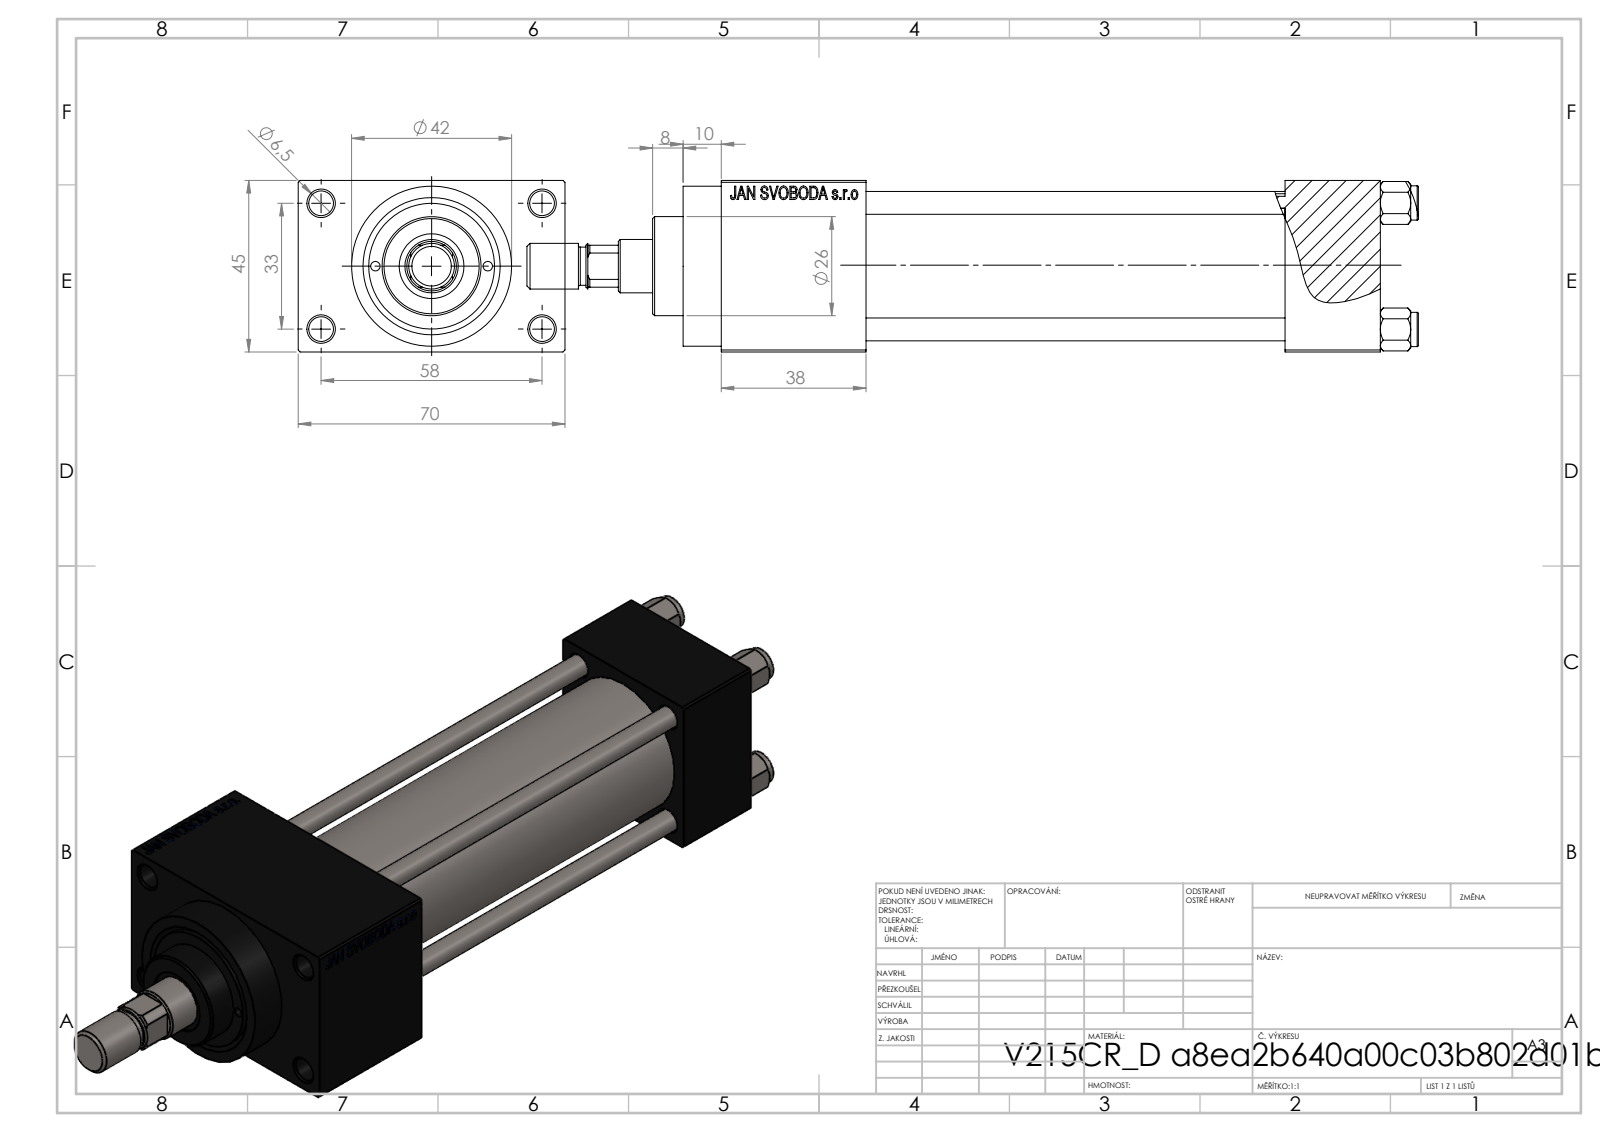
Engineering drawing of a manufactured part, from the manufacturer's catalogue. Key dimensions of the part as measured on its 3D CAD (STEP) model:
Part name (STEP PRODUCT): ROD_END_AH; V215CR_D_Body; V215_VC_A; NUT_M5_D (+2 more)
STEP written by: SolidWorks 2019 (CONFIG_CONTROL_DESIGN)
Units: millimetres
Bodies: 12 solids, 1124 faces (502 planar, 96 cylindrical, 526 other)
Overall size (bounding box): 234 × 70 × 45
Volume: 267 698 mm³ · Surface area: 96 586 mm²
Round holes (diameter × count): ⌀6.5 ×5, ⌀6 ×4, ⌀2.5 ×2, ⌀7 ×2, ⌀13.16 ×2, ⌀20 ×2, ⌀14 ×1, ⌀17 ×1, ⌀24 ×1, ⌀32 ×1, ⌀33 ×1
Round bosses / shafts (diameter × count): ⌀9 ×4, ⌀42 ×1, ⌀38 ×1, ⌀26 ×1, ⌀12 ×1, ⌀10 ×1
Partial cylindrical surfaces — rounded edges, fillets, slot ends (radius × count): R6.5 ×1
Main face-to-face distances: 45, 25, 12.5, 110, 135, 57.5, 148, 38, 173, 70
Hole centre spacings: 12.4, 16.7, 21.8, 23.48, 33.2, 33.37, 35.35, 35.47
